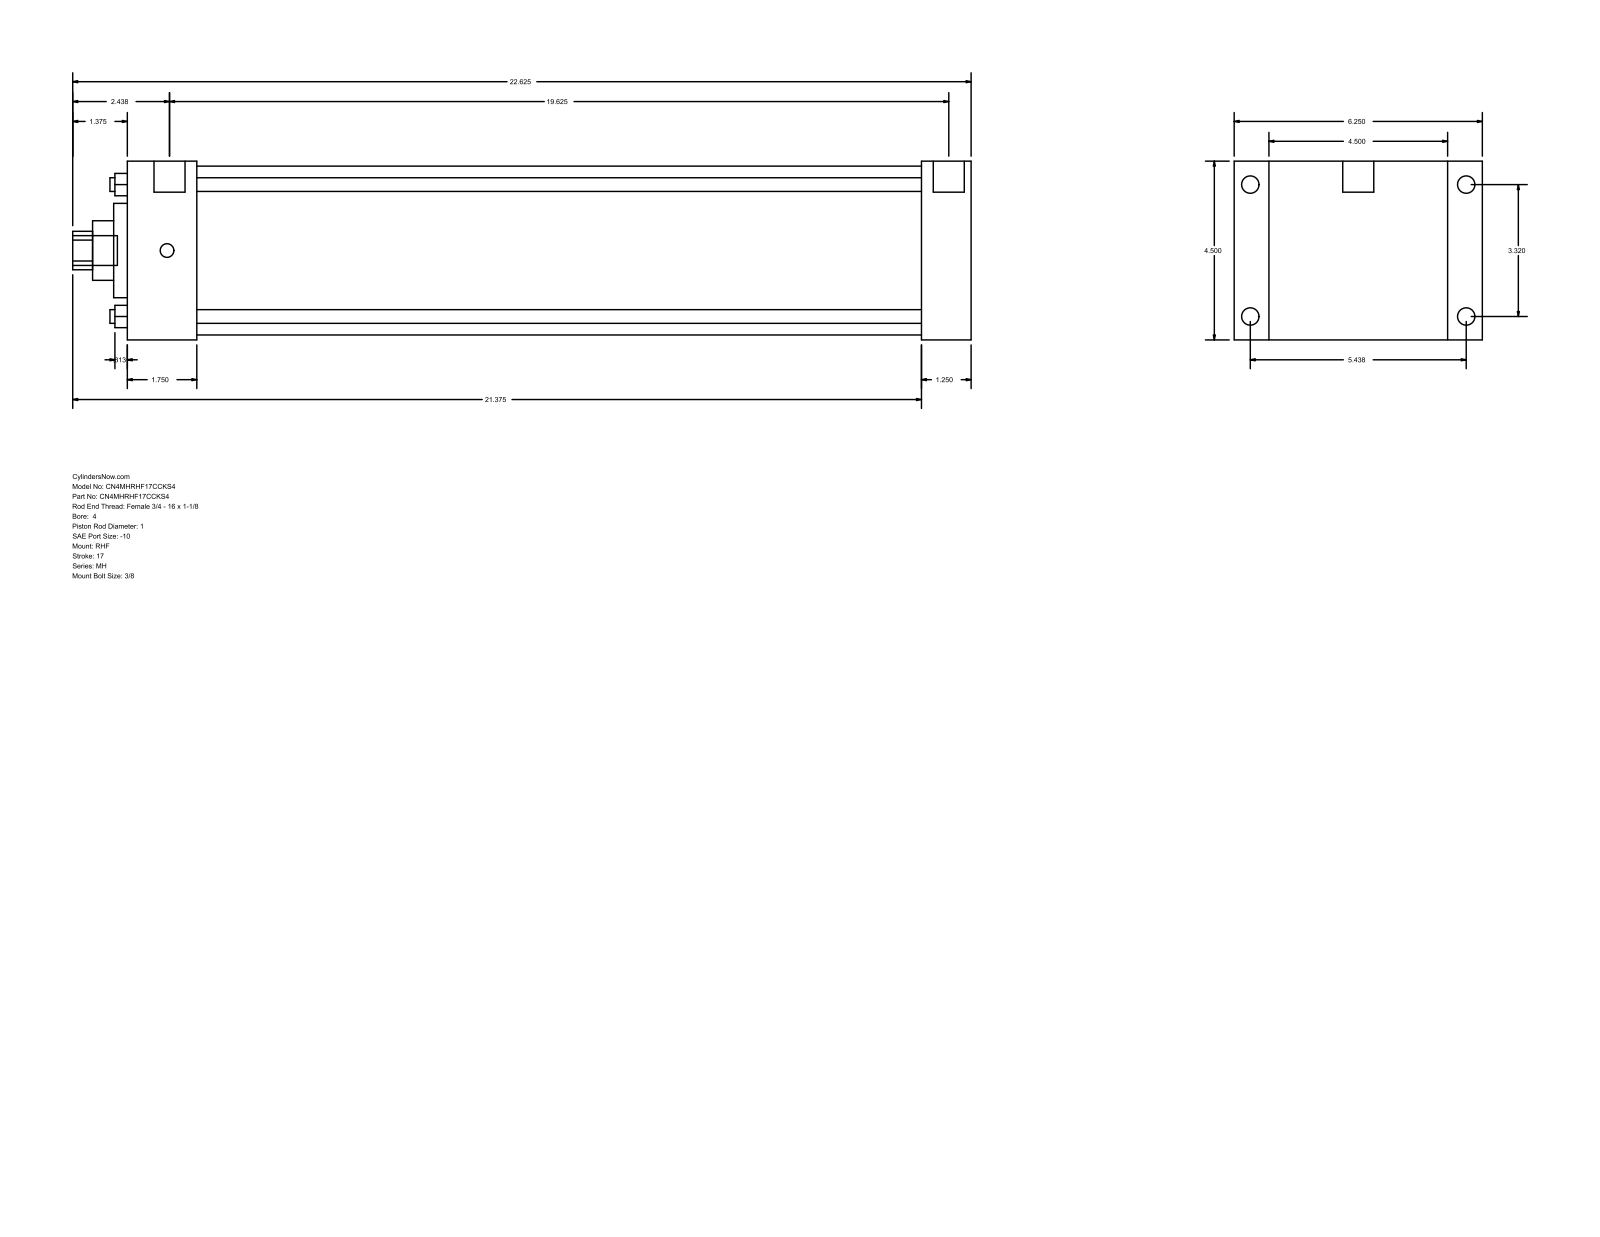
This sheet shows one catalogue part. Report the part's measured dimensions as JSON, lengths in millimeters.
{"part_name": "MH_RHF__0400_1", "step_written_by": "GSSL Pune (CONFIG_CONTROL_DESIGN)", "units": "millimeters", "bodies": {"solids": 0, "faces": 90, "planar": 61, "cylindrical": 29, "other": 0}, "overall_size": [574.67, 158.75, 114.3], "round_holes": [[8.76, 4], [25.4, 1], [38.1, 1], [60.33, 1], [107.95, 1]], "round_bosses_or_shafts": [[11.13, 4], [8.73, 4], [19.84, 2], [19.05, 1]], "partial_cylinders_radius": [[12.29, 1]], "face_to_face_distances": [114.3, 539.75, 508, 31.75, 22.23, 136.53, 44.46, 463.54, 495.29, 158.76], "hole_center_spacings": [59.62, 84.32, 119.25]}
